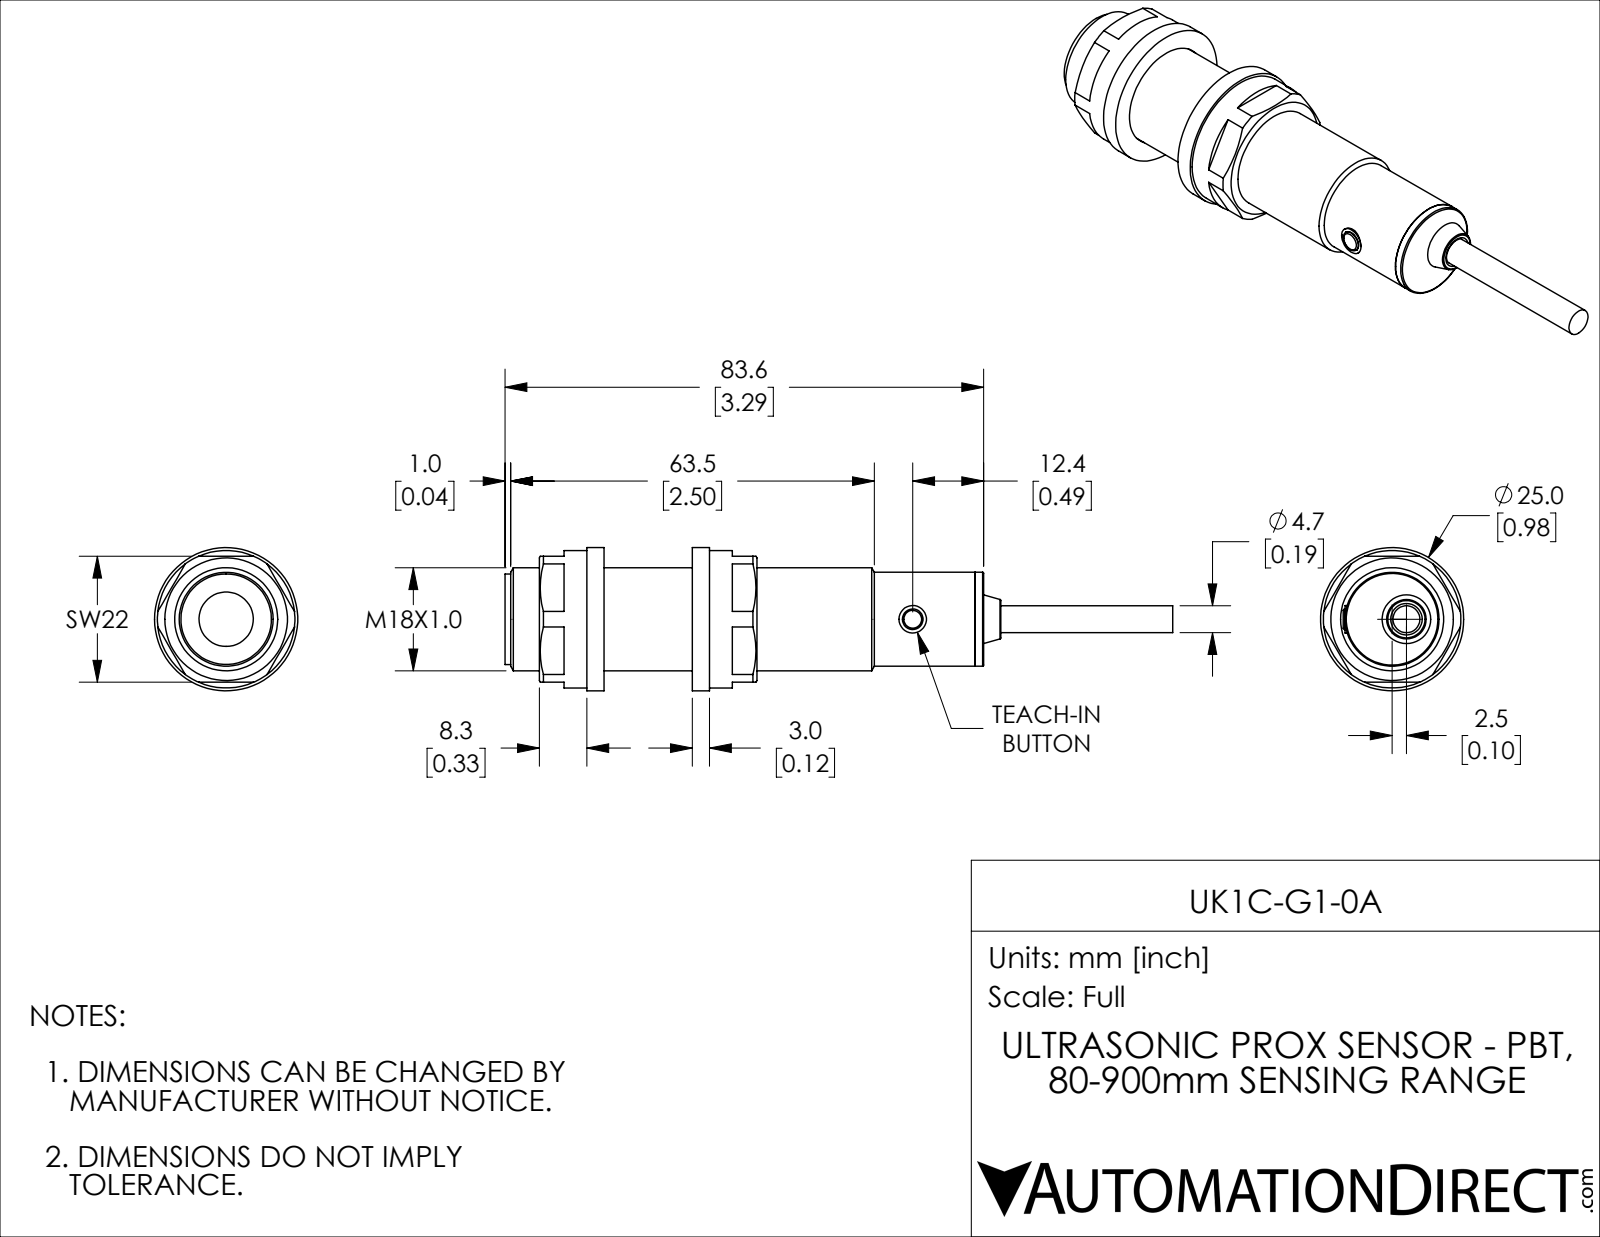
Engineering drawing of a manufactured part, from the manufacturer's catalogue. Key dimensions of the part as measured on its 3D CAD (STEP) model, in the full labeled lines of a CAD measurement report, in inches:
Part name (STEP PRODUCT): UK1C-G1-0A
STEP written by: SolidWorks 2018 (AUTOMOTIVE_DESIGN)
Units: inches
Bodies: 10 solids, 107 faces (49 planar, 40 cylindrical, 18 other)
Overall size (bounding box): 4.591 × 0.984 × 0.984
Volume: 1.539 in³ · Surface area: 17.7 in²
Round holes (diameter × count): ⌀0.185 ×2, ⌀0.142 ×1, ⌀0.374 ×1, ⌀0.709 ×1, ⌀0.717 ×1
Round bosses / shafts (diameter × count): ⌀0.984 ×1, ⌀0.945 ×1, ⌀0.646 ×1, ⌀0.622 ×1, ⌀0.213 ×1, ⌀0.189 ×1
Main face-to-face distances: 0.118, 0.724, 0.843, 2.669, 1.827, 0.524, 1.366, 3.193, 0.642, 2.551
Hole centre spacings: 0.098
